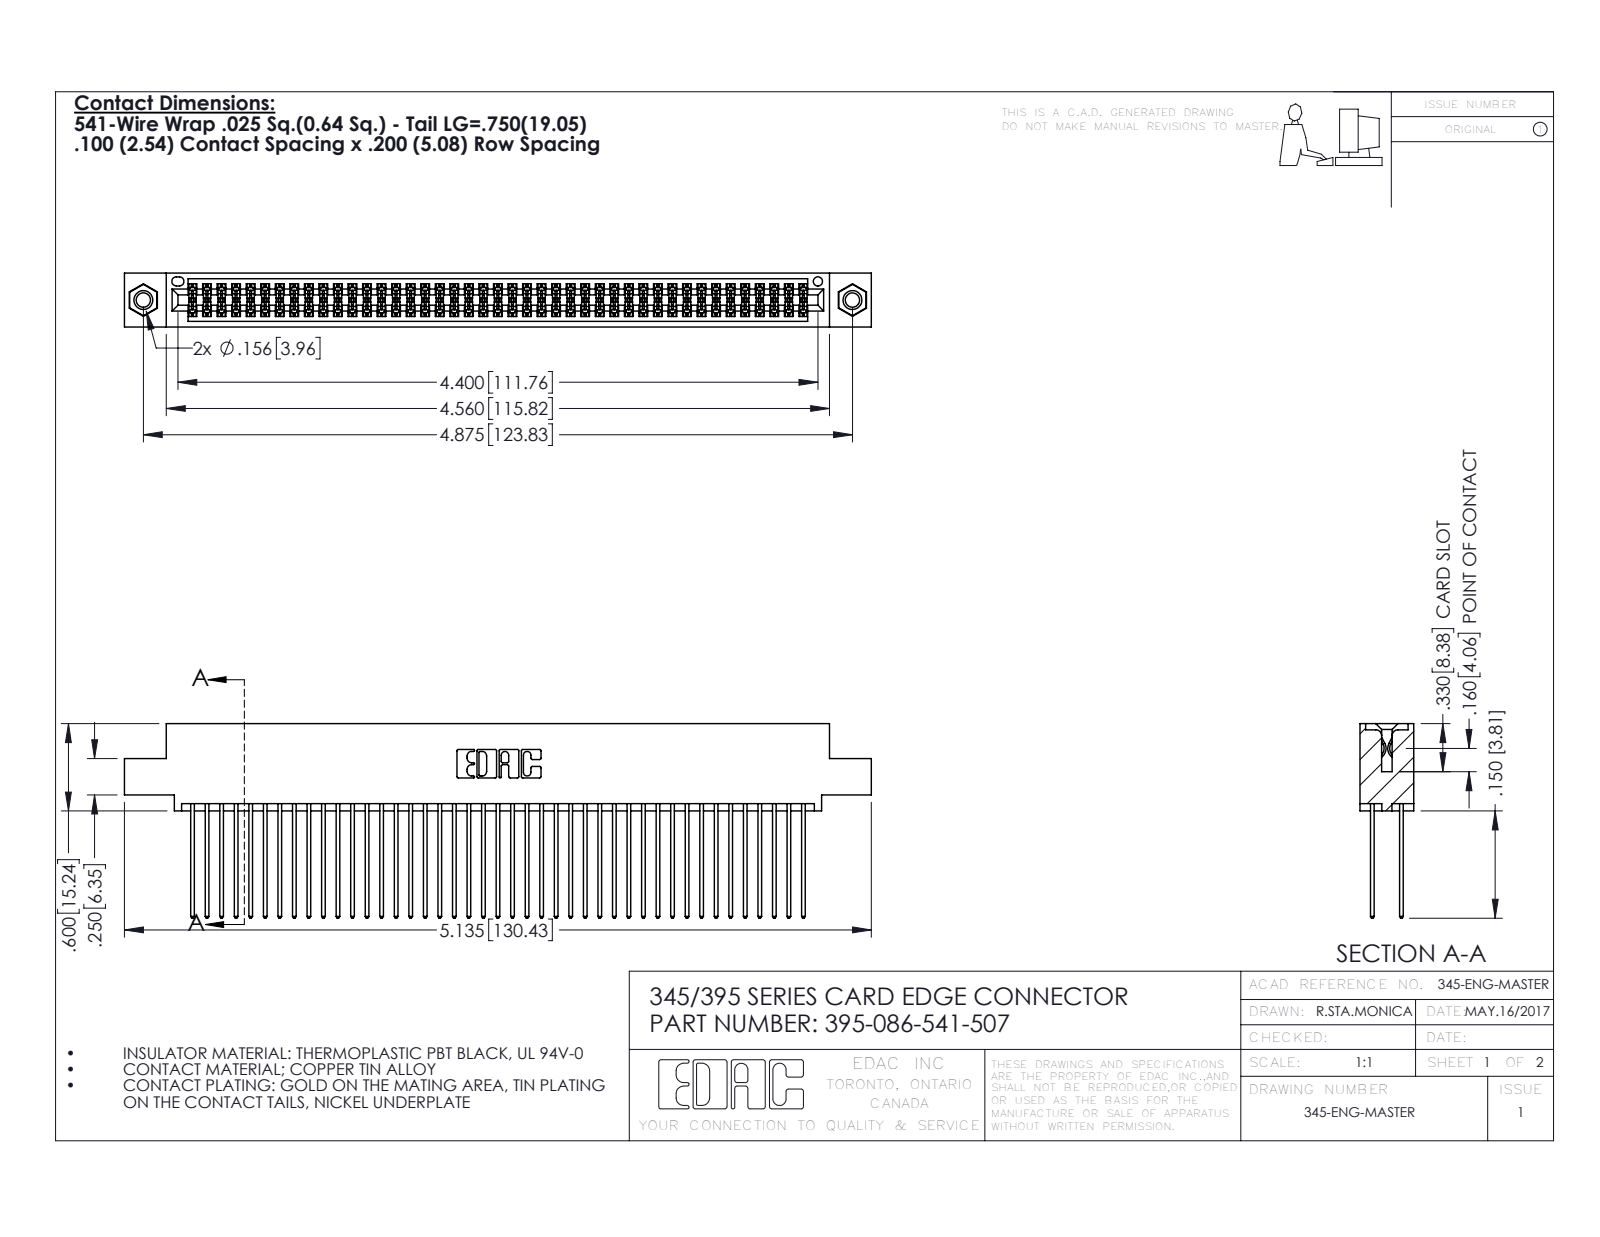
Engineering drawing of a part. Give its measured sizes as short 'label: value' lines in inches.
name: 395-086-541-507; 345 Part_0.110 Offset - 0.156 Dia-TI; 345-250-001_345-250-005-103; 345-292-001_345-293-141
written by: SolidWorks 2016 (CONFIG_CONTROL_DESIGN)
unit: in
bodies: 89 solids, 4490 faces (2954 planar, 1520 cylindrical, 16 other)
size: 5.135 × 1.337 × 0.37
volume: 0.799 in³; area: 33.79 in²
holes: 2× ⌀0.098, 2× ⌀0.125, 2× ⌀0.156, 1× ⌀0.064
bosses: 2× ⌀0.155
rounds: 129× R0.006, 86× R0.01, 22× R0.01, 6× R0.007, 6× R0.031, 3× R0.026, 2× R0.014, 2× R0.019
face distances: 0.072, 0.298, 0.2, 0.098, 0.272, 0.025, 0.225, 0.37, 0.175, 0.149
hole spacings: 0.27, 4.639, 4.875
